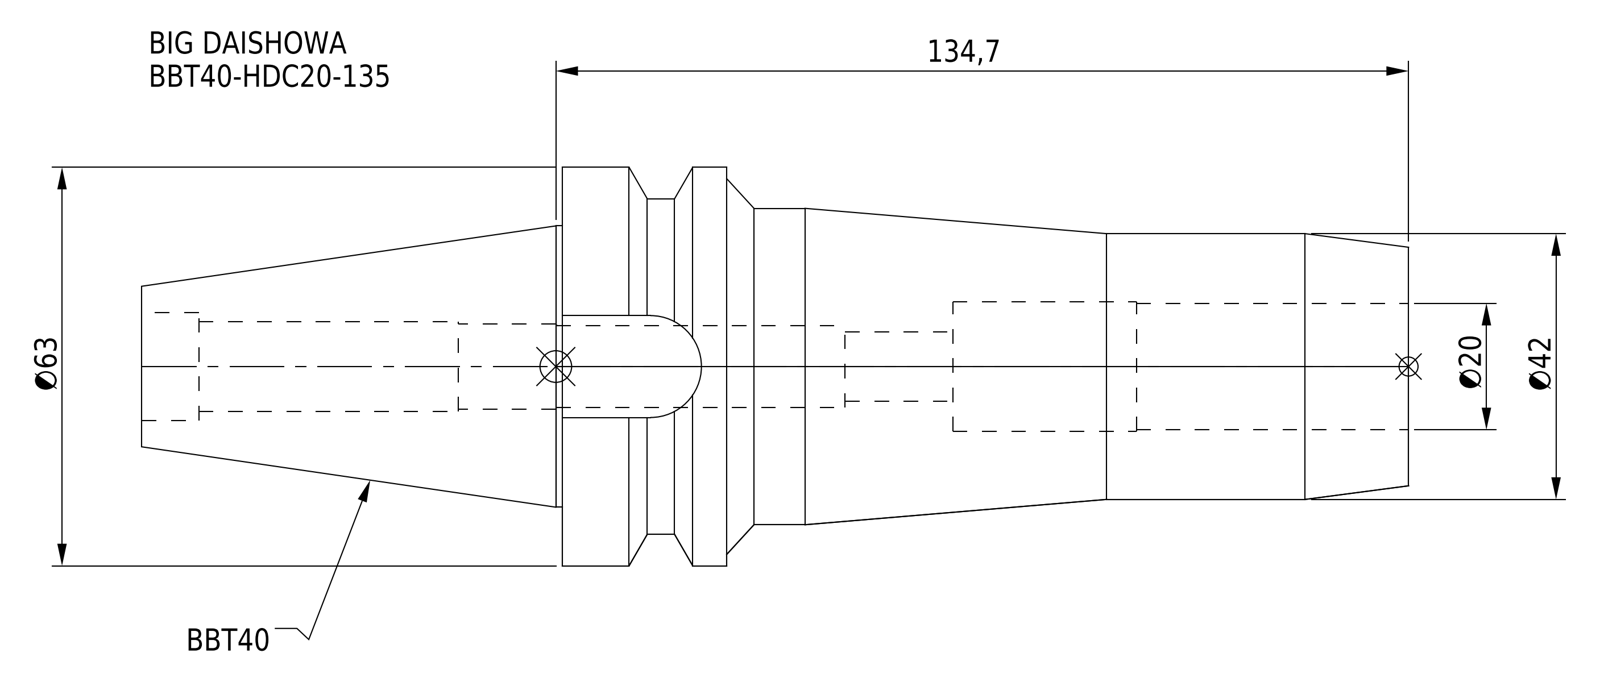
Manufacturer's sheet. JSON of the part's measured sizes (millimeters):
{"part_name": "BBT40-HDC20-135", "step_written_by": "CREO PARAMETRIC BY PTC INC, 2016380 (AUTOMOTIVE_DESIGN)", "units": "millimeters", "bodies": {"solids": 1, "faces": 59, "planar": 17, "cylindrical": 30, "other": 12}, "overall_size": [200.1, 63, 63], "volume_mm3": 263281, "surface_area_mm2": 42452, "round_holes": [[11, 1], [13, 1], [13.2, 1], [13.4, 1], [14.2, 1], [17, 1], [20, 1], [20.5, 1]], "round_bosses_or_shafts": [[63, 1], [53, 1], [50, 1], [44.45, 1], [42, 1]], "partial_cylinders_radius": [[8.05, 1]], "face_to_face_distances": [133.7, 107.7, 26, 45, 200.1, 92.4, 66.4, 72, 35.7, 61.7]}
